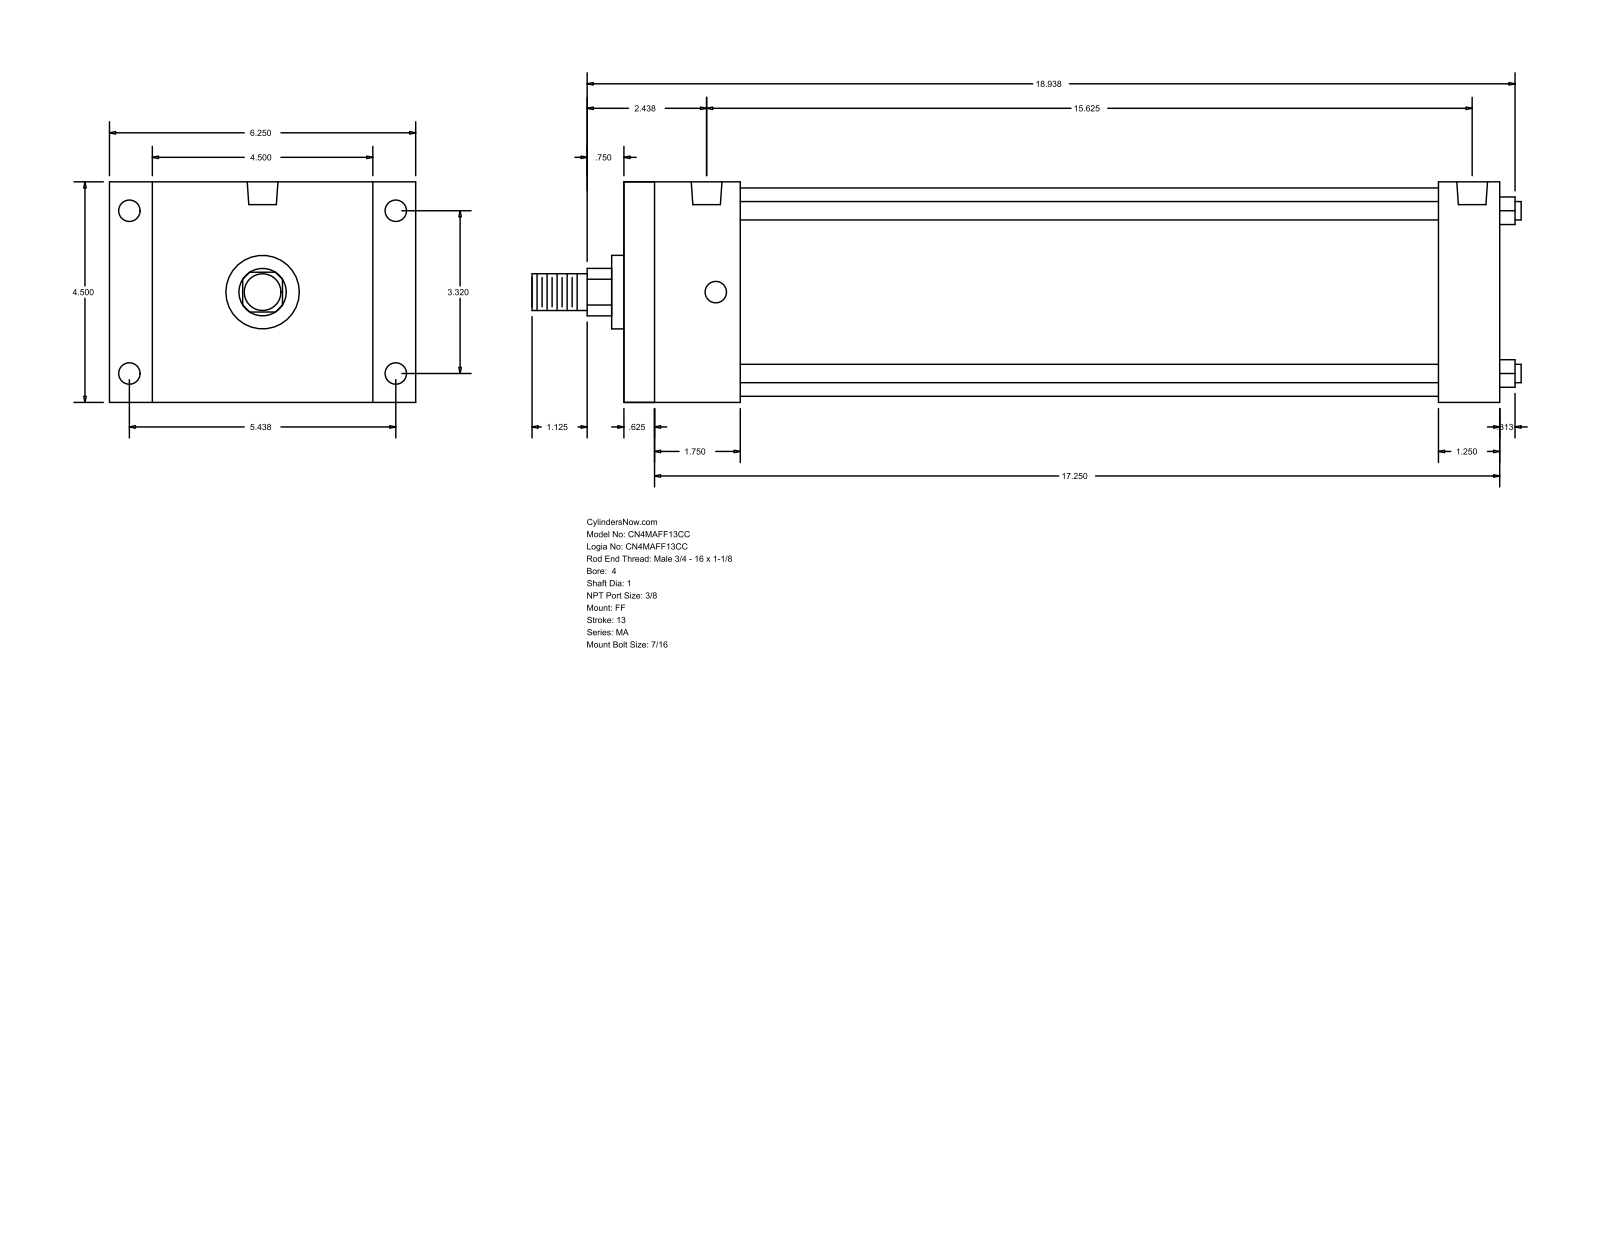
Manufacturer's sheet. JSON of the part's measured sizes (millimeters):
{"part_name": "MA_FF__0400_1", "step_written_by": "GSSL Pune (CONFIG_CONTROL_DESIGN)", "units": "millimeters", "bodies": {"solids": 0, "faces": 92, "planar": 64, "cylindrical": 28, "other": 0}, "overall_size": [512.76, 158.75, 114.3], "round_holes": [[11.11, 8], [15.93, 2]], "round_bosses_or_shafts": [[9.53, 4], [107.95, 1], [38.1, 1], [25.4, 1], [19.05, 1]], "partial_cylinders_radius": [[12.29, 1]], "face_to_face_distances": [114.3, 454.02, 15.87, 438.15, 22.23, 136.53, 422.27, 406.4, 31.75, 60.33], "hole_center_spacings": [84.32, 138.12, 161.82, 387.35, 4.76, 4.77, 392.11, 392.12]}
